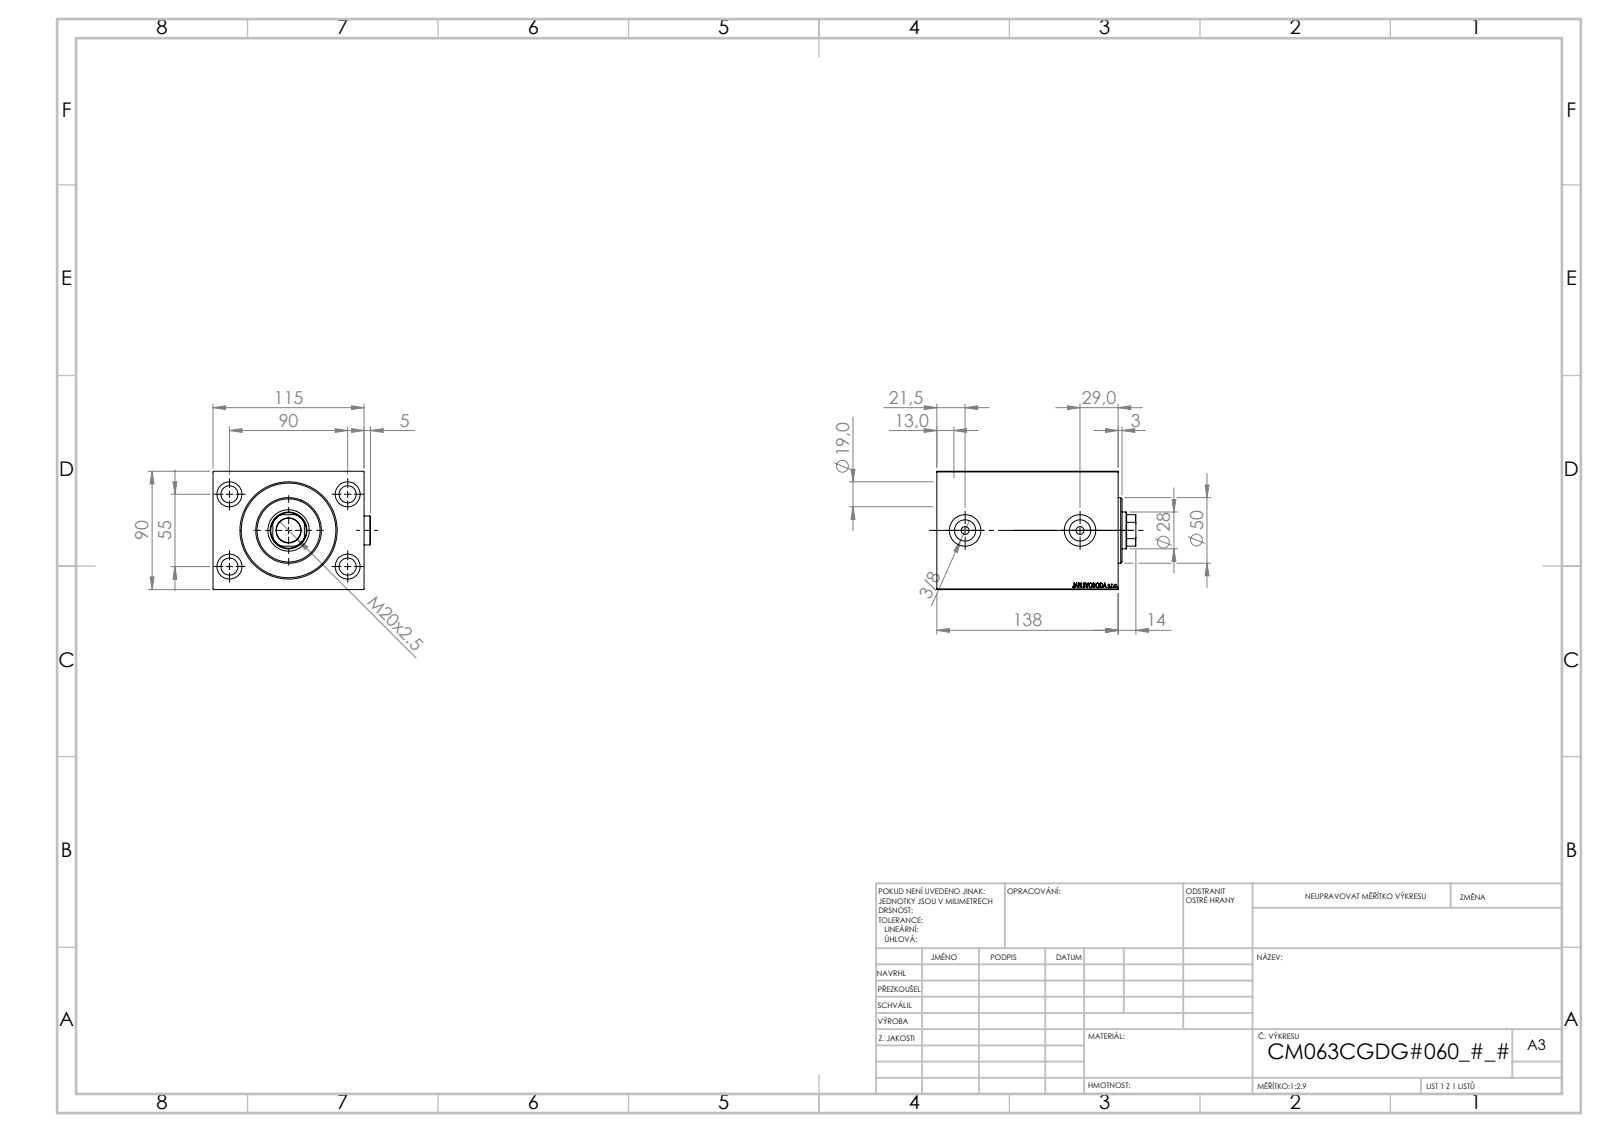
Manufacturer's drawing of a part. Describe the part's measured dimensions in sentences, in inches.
The part is named "V450CM_VC_B; V450CM_C_Body; V450CM_C_VCP; Zatka_OIL_PORT". Its 3-D file was written by "SolidWorks 2019 (CONFIG_CONTROL_DESIGN)". It is 5 solids with 919 faces: 443 planar, 78 cylindrical and 398 other. Overall it measures 5.965 by 4.72 by 3.543 inches. Its volume is 72.25 cubic inches and its surface area 258.2 square inches. Round holes: 4 of diameter 0.512, 4 of diameter 0.748, 2 of diameter 0.236, 2 of diameter 0.637, 2 of diameter 0.945, 1 of diameter 0.728, 1 of diameter 1.102, 1 of diameter 1.24, 1 of diameter 2.48, 1 of diameter 2.559, 1 of diameter 2.835. Round bosses or shafts: 2 of diameter 0.866, 1 of diameter 1.969. Partial cylindrical surfaces (rounded edges, fillets, slot ends): 1 of radius 0.531. The main face-to-face distances are 3.543, 4.528, 5.433, 0.689, 4.744, 0.531, 4.213, 4.902, 2.539, 2.894. The hole center spacings are 2.076, 2.165, 3.543, 4.153, 3.445.
